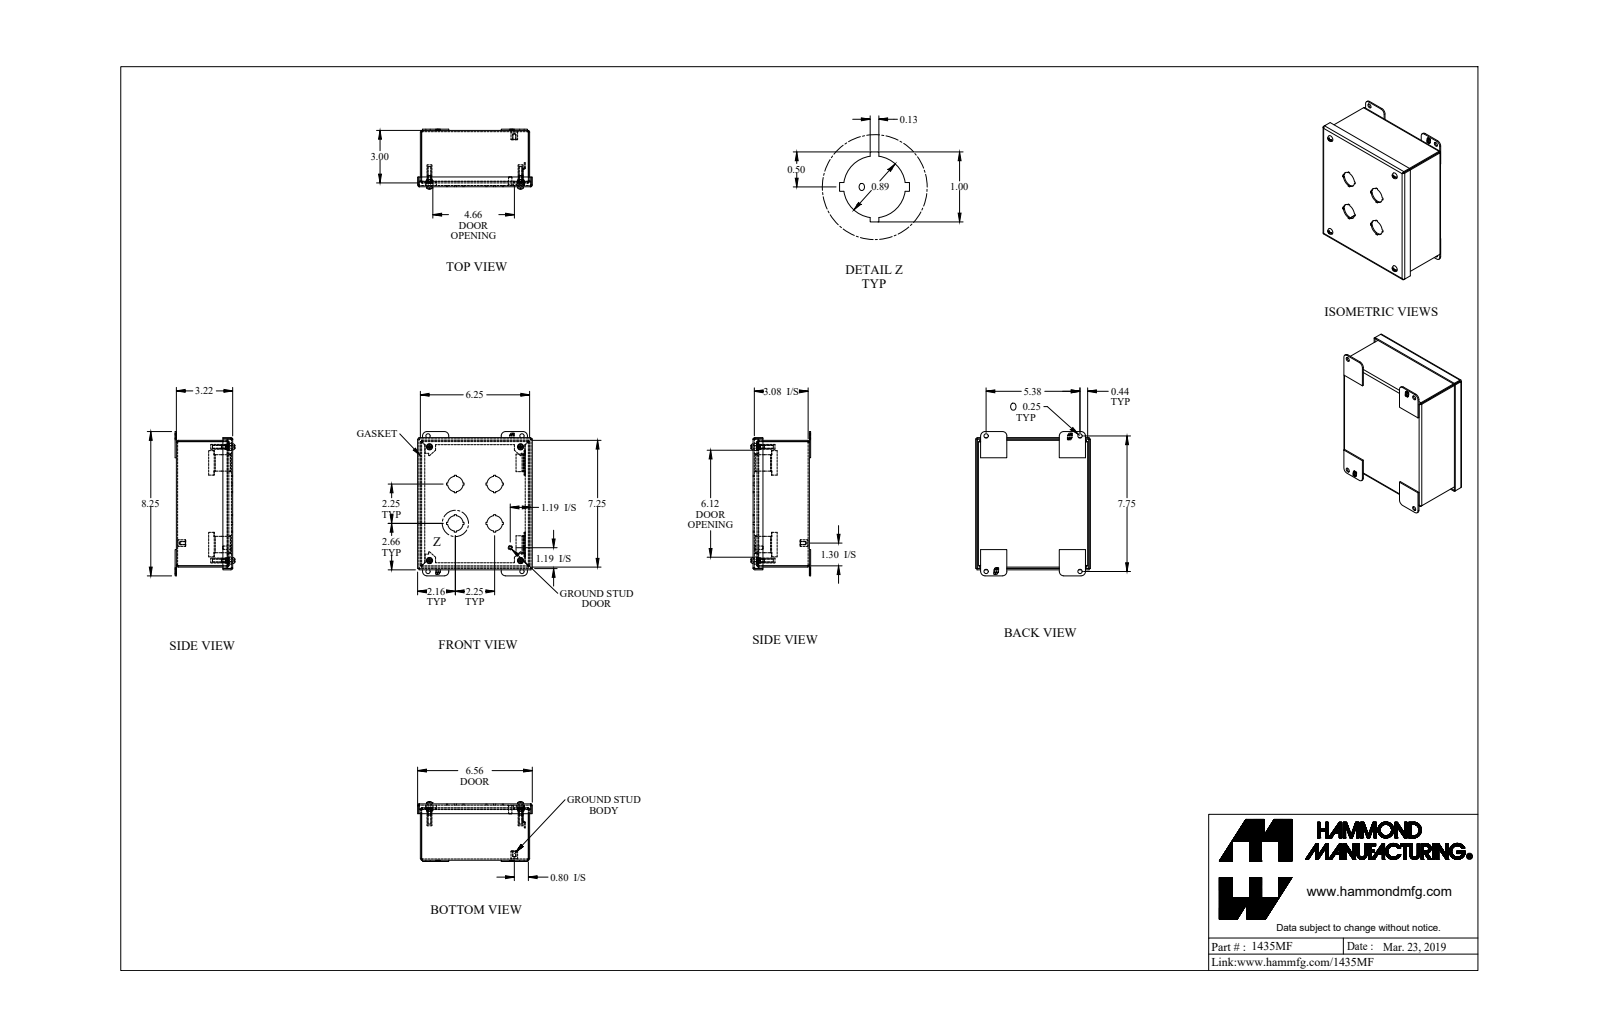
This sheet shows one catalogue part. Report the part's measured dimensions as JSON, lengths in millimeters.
{"part_name": "1435MF_Default", "step_written_by": "SolidWorks 2019 (CONFIG_CONTROL_DESIGN)", "units": "millimeters", "bodies": {"solids": 23, "faces": 779, "planar": 547, "cylindrical": 176, "other": 56}, "overall_size": [209.6, 166.7, 86.9], "volume_mm3": 280700, "surface_area_mm2": 292600, "round_holes": [[6.4, 8], [4, 4], [10.3, 4], [22.5, 4], [4, 1]], "round_bosses_or_shafts": [[9.9, 4], [7, 4], [4.8, 4], [3.8, 4], [9.5, 1], [6.4, 1], [4.8, 1]], "partial_cylinders_radius": [[0.9, 12], [2.7, 12], [6.4, 8], [0.7, 4], [2.2, 4], [4.1, 4], [4.3, 4]], "face_to_face_distances": [1.8, 80, 81.8, 78.2, 156.9, 182.3, 4, 158.8, 155.1, 180.5], "hole_center_spacings": [165.1, 181, 117.3, 16, 57.2, 65.8, 132.3, 132.4]}
